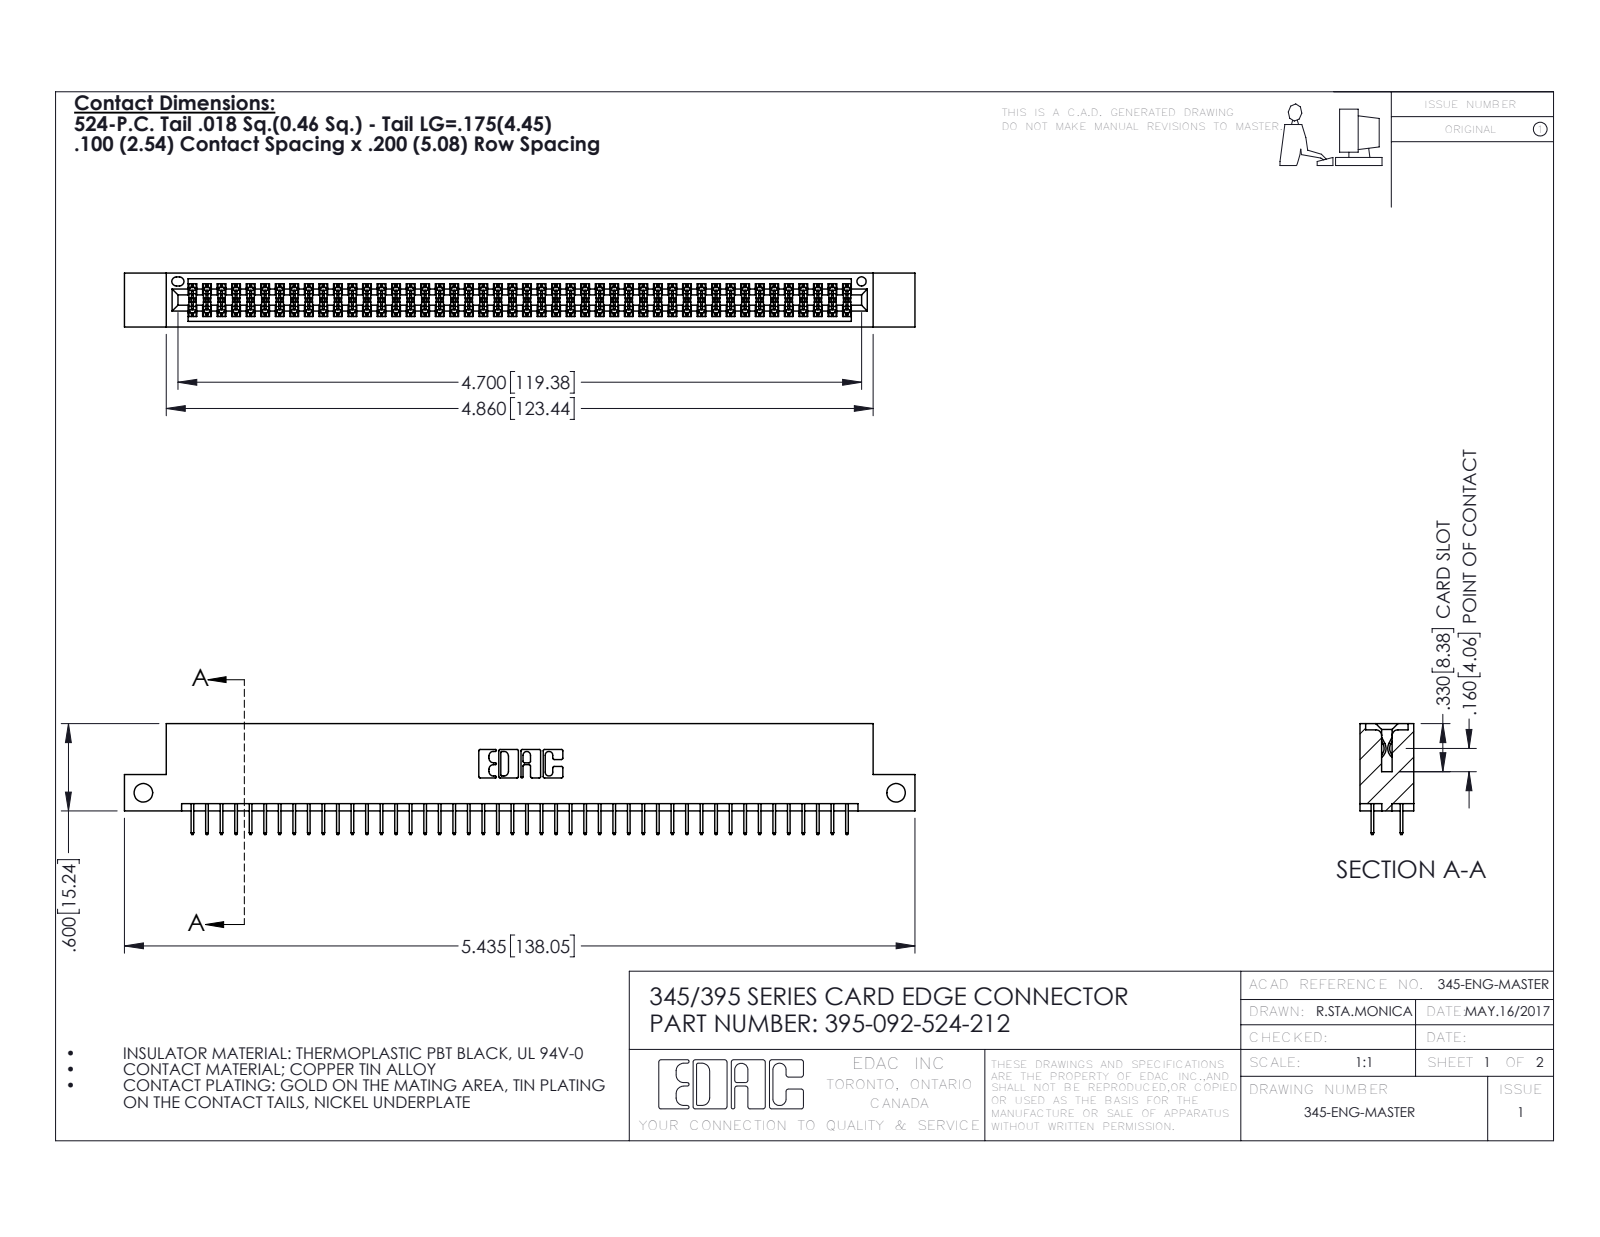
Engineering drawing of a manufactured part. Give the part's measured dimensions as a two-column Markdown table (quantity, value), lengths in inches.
| quantity | value |
| --- | --- |
| part name | 345-292-001_345-293-124; 395-092-524-212; 345 Part_Flush Mounting Lugs - Side Mount |
| STEP written by | SolidWorks 2016 (CONFIG_CONTROL_DESIGN) |
| units | inches |
| bodies | 93 solids, 5094 faces (3668 planar, 1426 cylindrical, 0 other) |
| overall size | 5.435 × 0.762 × 0.37 |
| volume | 0.807 in³ |
| surface area | 29.63 in² |
| round holes (diameter × count) | 0.128 × 2, 0.064 × 1 |
| partial cylindrical surfaces (radius × count) | 0.006 × 138, 0.01 × 22, 0.007 × 6, 0.031 × 6, 0.026 × 3, 0.014 × 2, 0.019 × 2, 0.022 × 2 |
| main face-to-face distances | 0.298, 0.072, 0.2, 0.37, 0.098, 0.272, 0.025, 0.225, 0.072, 0.175 |
| hole center spacings | 5.175 |
